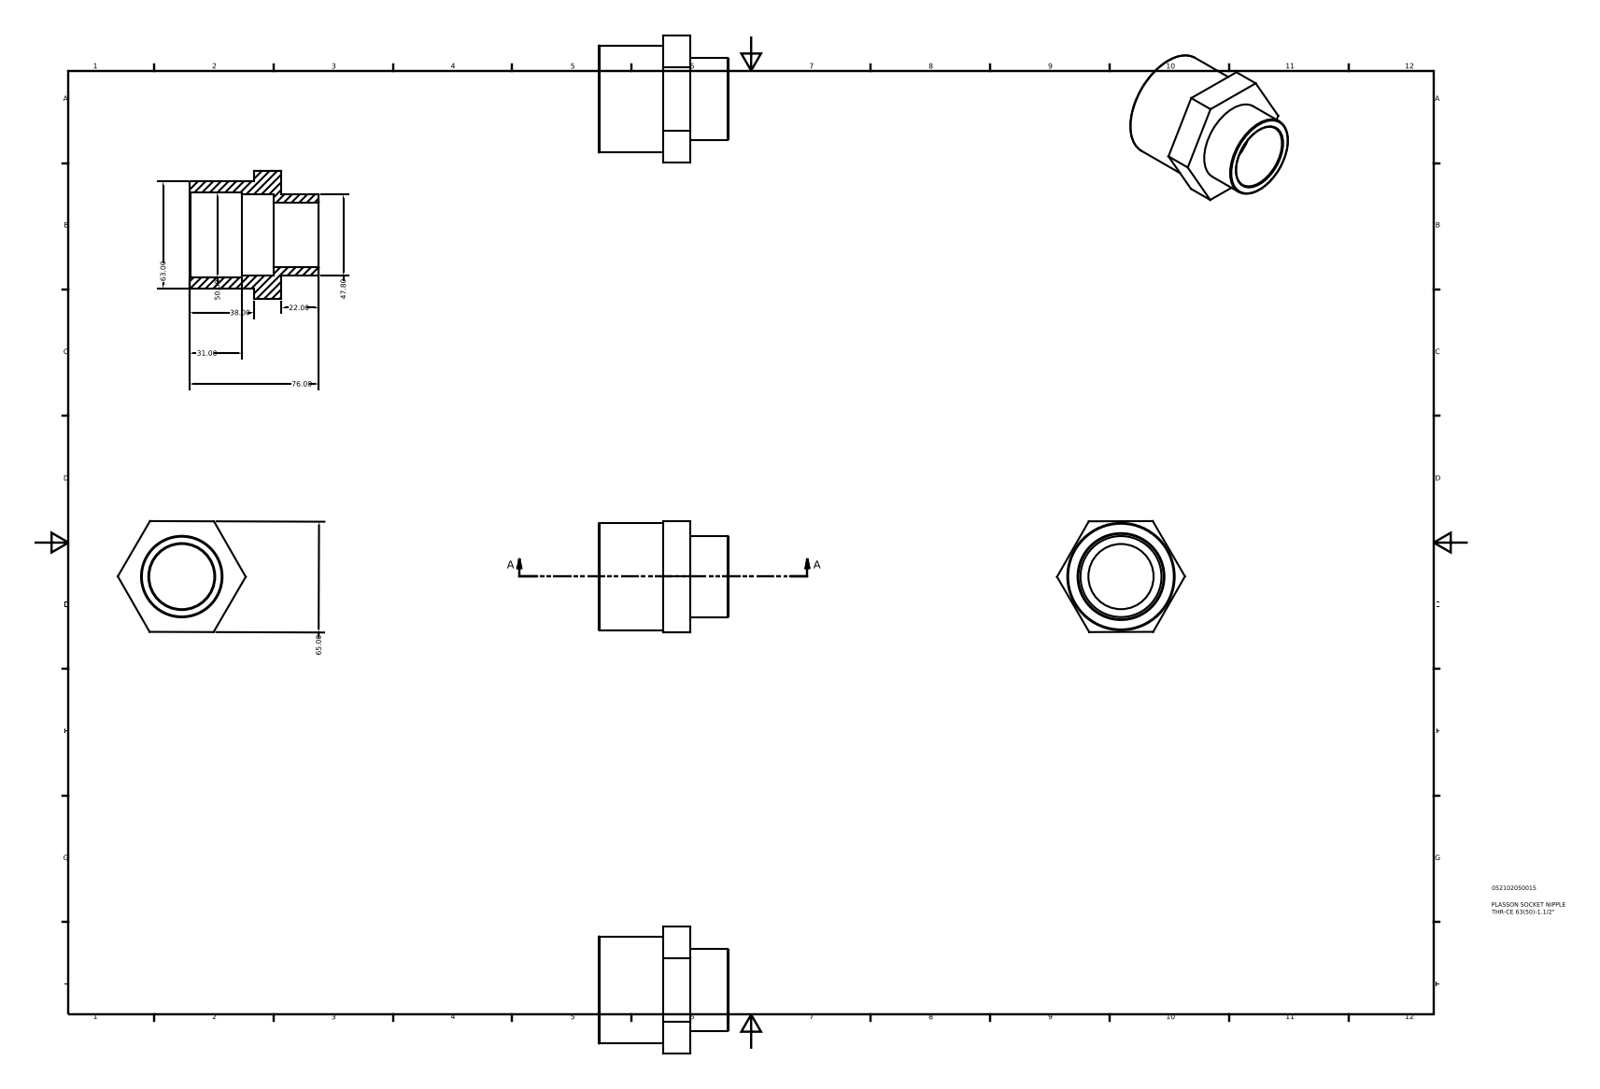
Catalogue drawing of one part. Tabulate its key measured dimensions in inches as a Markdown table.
| quantity | value |
| --- | --- |
| part name | 052102050015 |
| STEP written by | Autodesk Inventor 2015 (AUTOMOTIVE_DESIGN) |
| units | inches |
| bodies | 1 solid, 21 faces (12 planar, 5 cylindrical, 4 other) |
| overall size | 2.992 × 2.955 × 2.565 |
| volume | 5.632 in³ |
| surface area | 46.7 in² |
| round holes (diameter × count) | 1.506 × 1, 1.87 × 1, 1.969 × 1 |
| round bosses / shafts (diameter × count) | 2.48 × 1, 1.882 × 1 |
| main face-to-face distances | 1.496, 2.126, 1.953, 0.173, 2.558, 2.56, 2.559, 0.457, 0.63, 2.992 |
